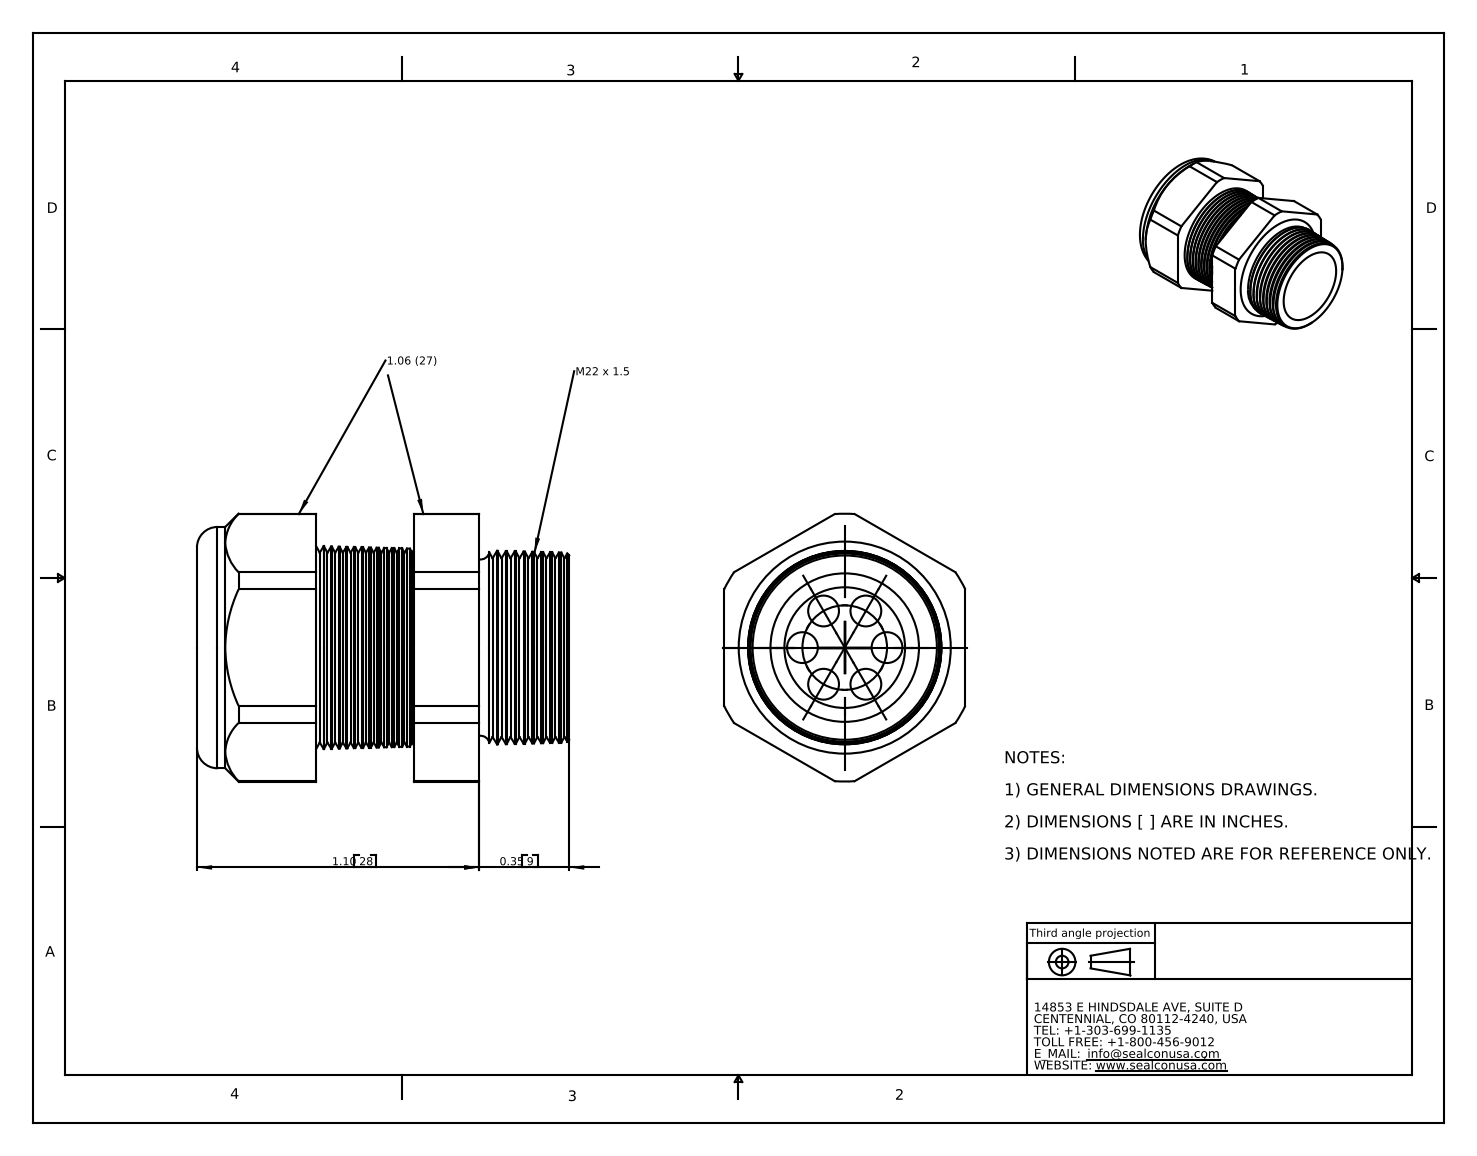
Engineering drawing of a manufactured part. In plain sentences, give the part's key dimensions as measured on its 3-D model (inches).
The part is named "CD22M8-GY". Its 3-D file was written by "SolidWorks 2007 (CONFIG_CONTROL_DESIGN)". It is 2 solids with 198 faces: 20 planar, 32 cylindrical and 146 other. Overall it measures 1.45 by 1.043 by 0.94 inches. Its volume is 0.579 cubic inches and its surface area 10.41 square inches. Round holes: 6 of diameter 0.12, 1 of diameter 0.45, 1 of diameter 0.47. Round bosses or shafts: 1 of diameter 0.94. Partial cylindrical surfaces (rounded edges, fillets, slot ends): 1 of radius 0.522. The main face-to-face distances are 0.94, 0.844, 0.465, 0.38, 1.1, 0.635, 0.256, 1.45, 0.985, 0.606. The hole center spacings are 0.165, 0.285, 0.329.
